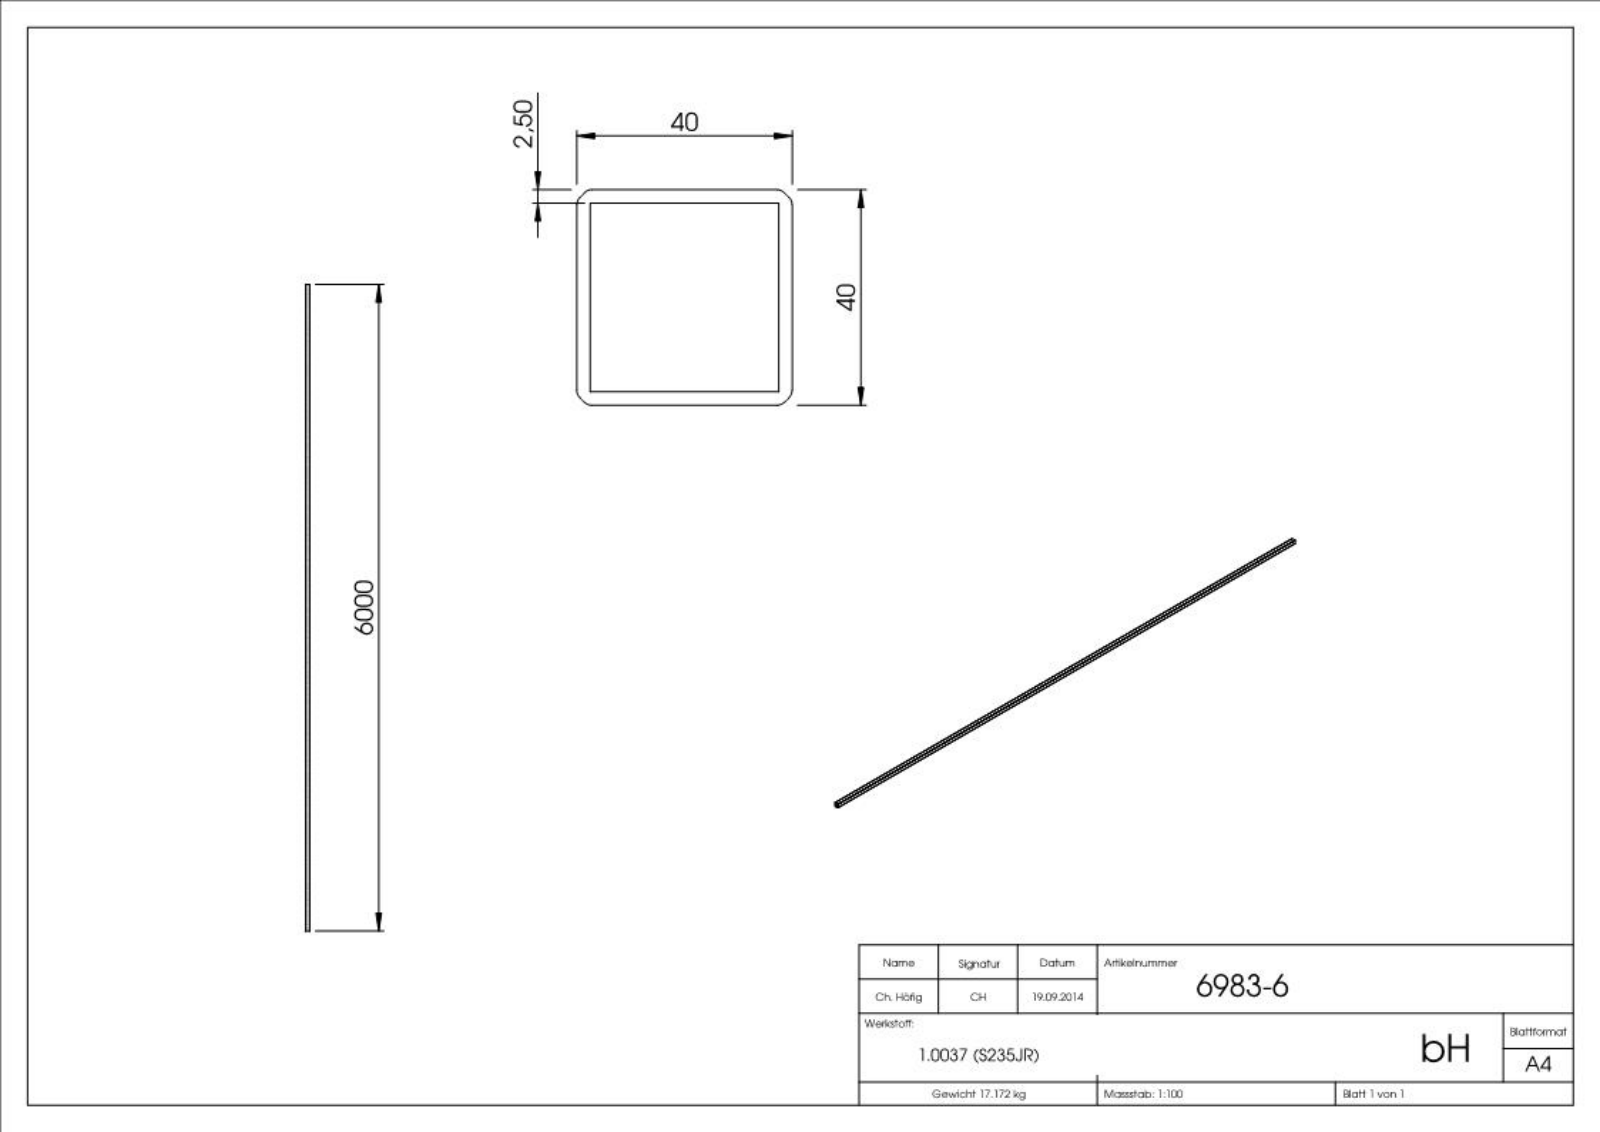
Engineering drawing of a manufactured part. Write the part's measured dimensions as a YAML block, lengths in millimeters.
part_name: "6983-6"
step_written_by: "SolidWorks 2018 (CONFIG_CONTROL_DESIGN)"
units: millimeters
bodies: {solids: 1, faces: 3622, planar: 104, cylindrical: 1108, other: 2410}
overall_size: [6000, 40, 40]
volume: 2176000
surface_area: 1745000
partial_cylinders:
  - {radius: 1.25, count: 4}
  - {radius: 3.75, count: 4}
face_to_face_distances: [2.5, 37.5, 40, 35, 6000, 5500, 500, 2.4, 35.1, 37.6]
